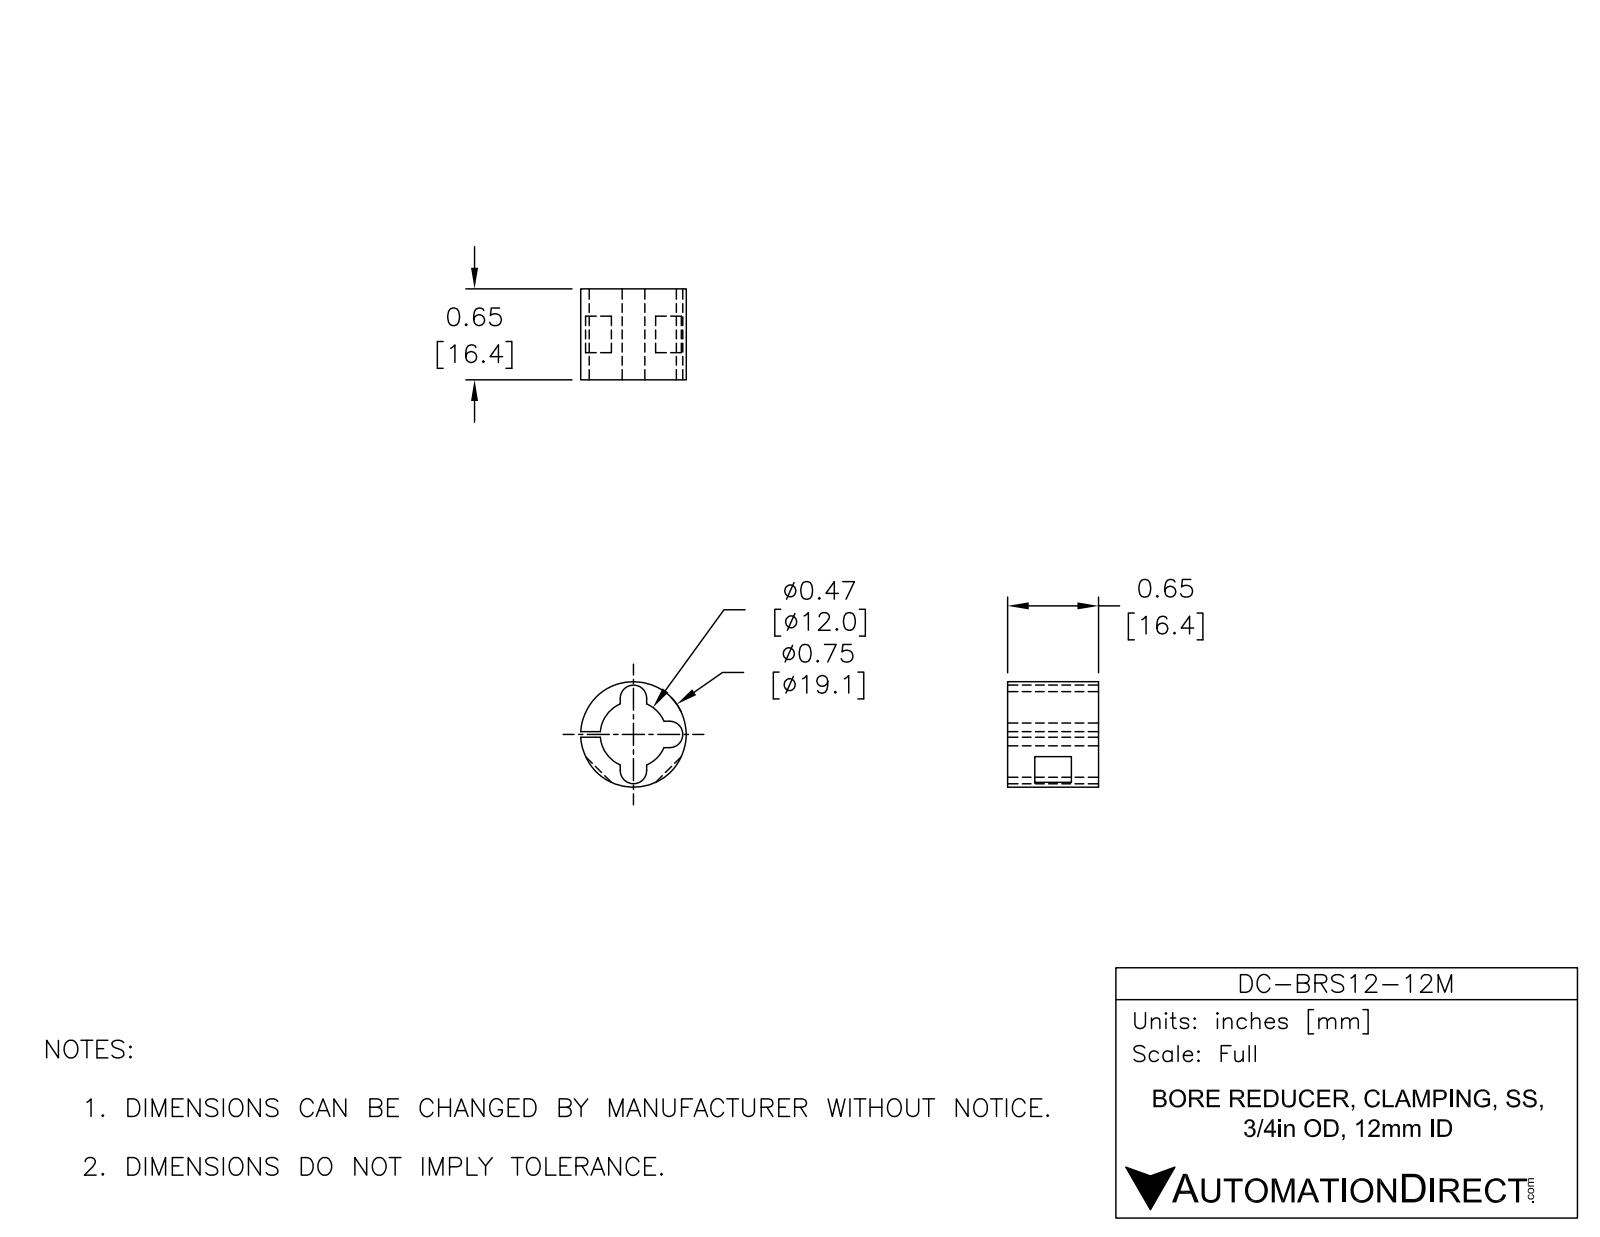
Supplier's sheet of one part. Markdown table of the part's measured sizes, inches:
| quantity | value |
| --- | --- |
| part name | DC-BRS12-12M |
| STEP written by | SolidWorks 2015 (AUTOMOTIVE_DESIGN) |
| units | inches |
| bodies | 1 solid, 27 faces (16 planar, 11 cylindrical, 0 other) |
| overall size | 0.75 × 0.75 × 0.646 |
| volume | 0.13 in³ |
| surface area | 3.382 in² |
| round bosses / shafts (diameter × count) | 0.75 × 1 |
| partial cylindrical surfaces (radius × count) | 0.094 × 3, 0.236 × 1 |
| main face-to-face distances | 0.646, 0.04, 0.187, 0.074, 0.114, 0.193, 0.453, 0.26 |
